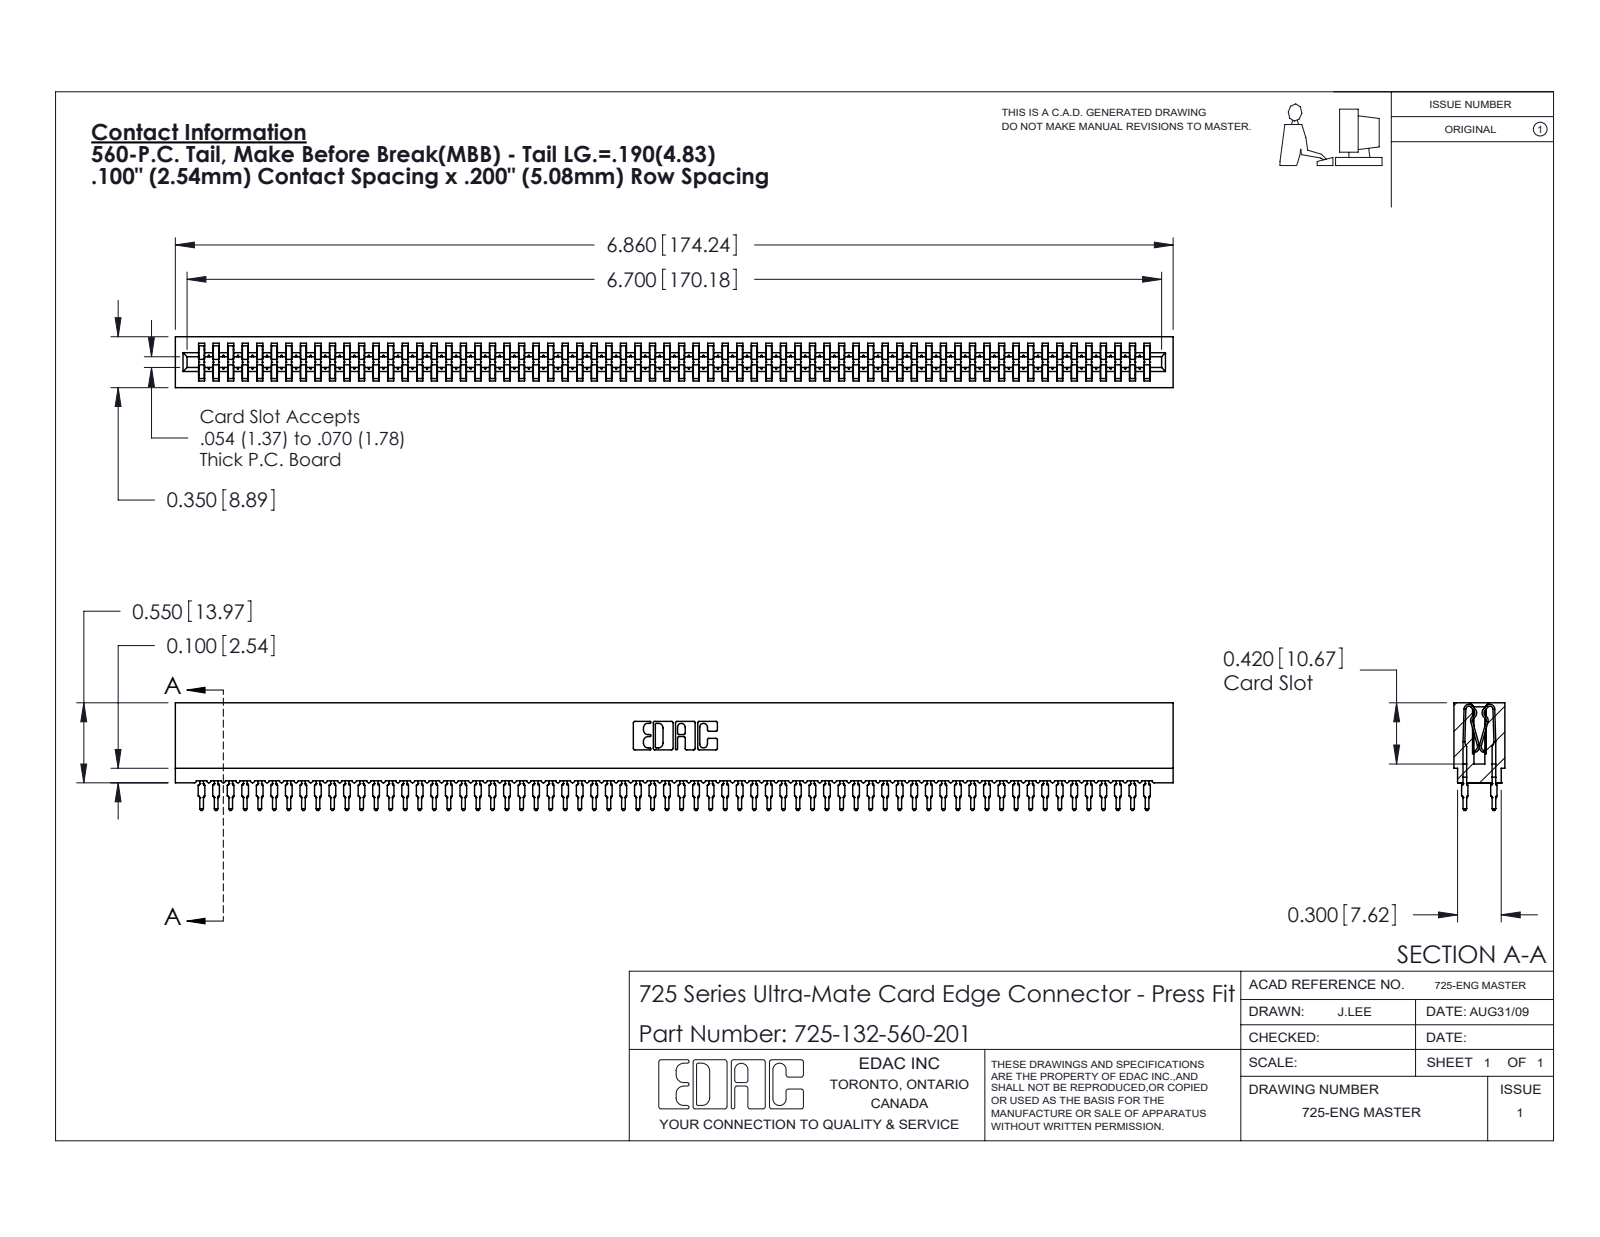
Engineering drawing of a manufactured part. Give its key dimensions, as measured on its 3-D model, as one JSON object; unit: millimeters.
{"part_name": "745-292-001_560; 725-132-560-201; 725 Part_Insulator Option - 01", "step_written_by": "SolidWorks 2020 (CONFIG_CONTROL_DESIGN)", "units": "millimeters", "bodies": {"solids": 133, "faces": 13097, "planar": 6787, "cylindrical": 2878, "other": 3432}, "overall_size": [174.2, 18.8, 8.9], "volume_mm3": 14200, "surface_area_mm2": 32560, "partial_cylinders_radius": [[0.5, 264], [0.4, 132], [0.3, 22], [0.1, 8], [0.3, 8], [0.2, 6], [0.8, 6], [0.7, 3]], "face_to_face_distances": [5.1, 1.6, 7.3, 8.9, 5.4, 3.5, 1.9, 3.8, 1.1, 7.7]}
